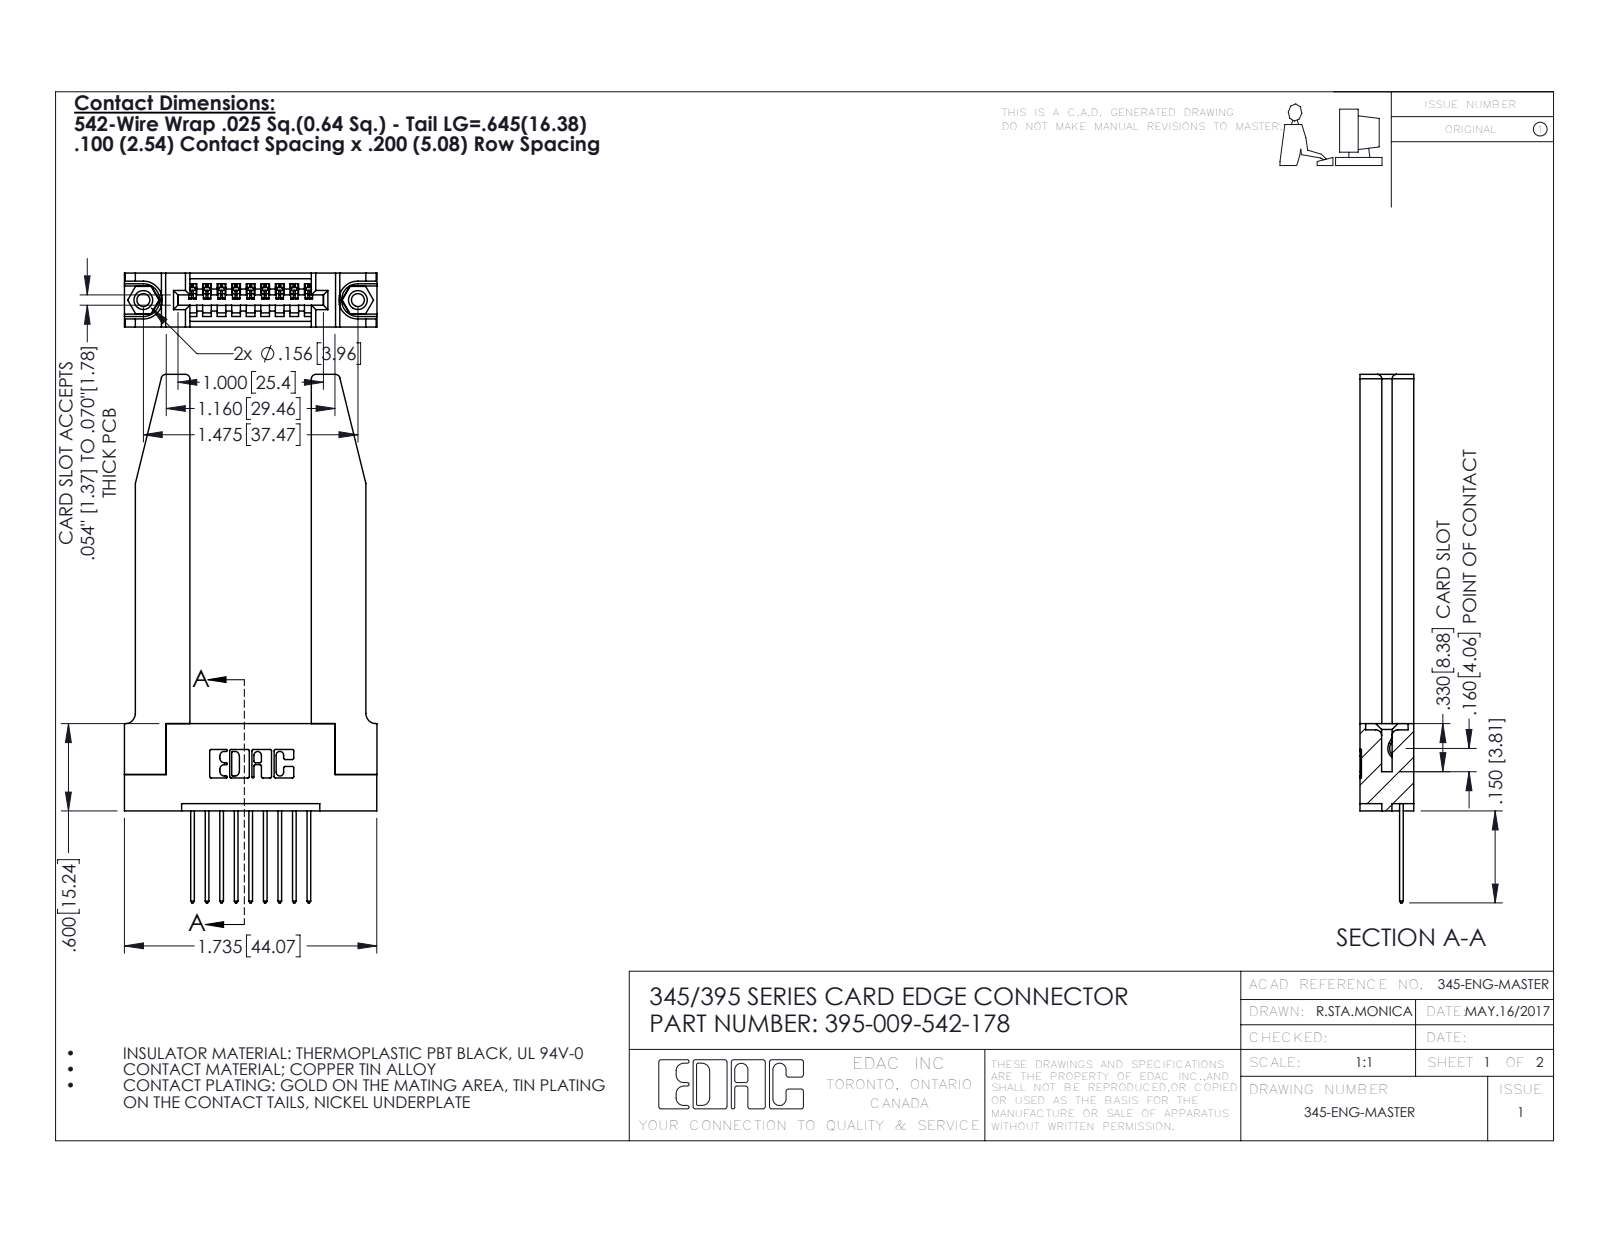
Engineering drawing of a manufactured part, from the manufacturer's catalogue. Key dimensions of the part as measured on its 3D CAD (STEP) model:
Part name (STEP PRODUCT): 395-009-542-178; 345 Part_Flush Mounting Lugs - 0.156 Dia-TH; 345-250-001_345-250-001-102; 345-292-001_345-293-142 (+1 more)
STEP written by: SolidWorks 2016 (CONFIG_CONTROL_DESIGN)
Units: inches
Bodies: 14 solids, 882 faces (582 planar, 248 cylindrical, 52 other)
Overall size (bounding box): 3.632 × 1.736 × 0.37
Volume: 0.714 in³ · Surface area: 18.22 in²
Round holes (diameter × count): ⌀0.089 ×2, ⌀0.125 ×2, ⌀0.156 ×2, ⌀0.064 ×1
Round bosses / shafts (diameter × count): ⌀0.155 ×2
Partial cylindrical surfaces — rounded edges, fillets, slot ends (radius × count): R0.01 ×22, R0.006 ×18, R0.01 ×18, R0.03 ×8, R0.007 ×6, R0.031 ×6, R0.026 ×3, R0.031 ×2
Main face-to-face distances: 0.37, 0.072, 0.298, 0.15, 0.148, 0.22, 0.2, 0.077, 0.835, 0.098
Hole centre spacings: 0.27, 1.244, 1.475
